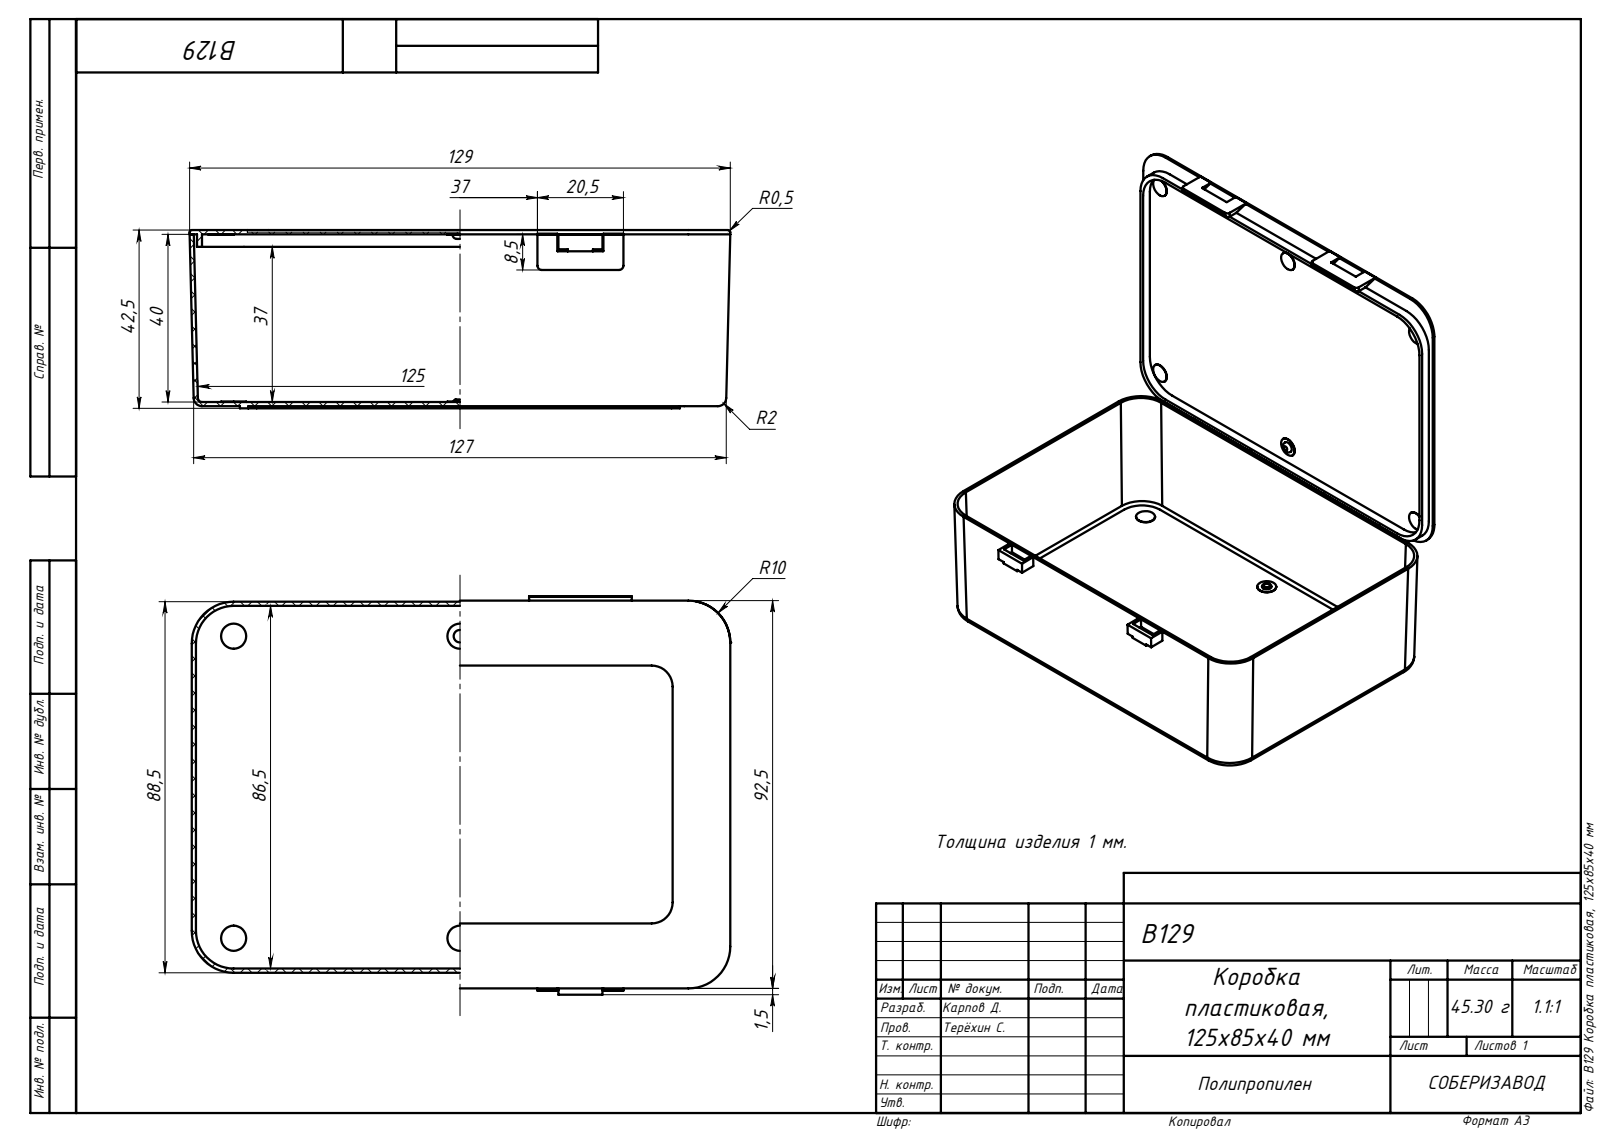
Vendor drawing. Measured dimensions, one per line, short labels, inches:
name: B129 Крышка; B129 Емкость; B129 Коробка пластиковая, 125x85x40 мм; B129 Защелка
written by: SolidWorks 2020 (AUTOMOTIVE_DESIGN)
unit: in
bodies: 5 solids, 235 faces (131 planar, 80 cylindrical, 24 other)
size: 5.079 × 3.74 × 1.673
volume: 2.349 in³; area: 129.3 in²
bosses: 12× ⌀0.236
rounds: 16× R0.394, 12× R0.079, 9× R0.039, 5× R0.02, 4× R0.004, 4× R0.197, 4× R0.354
face distances: 0.039, 1.614, 0.02, 1.575, 1.634, 1.594, 1.654, 0.047, 0.059, 1.673
